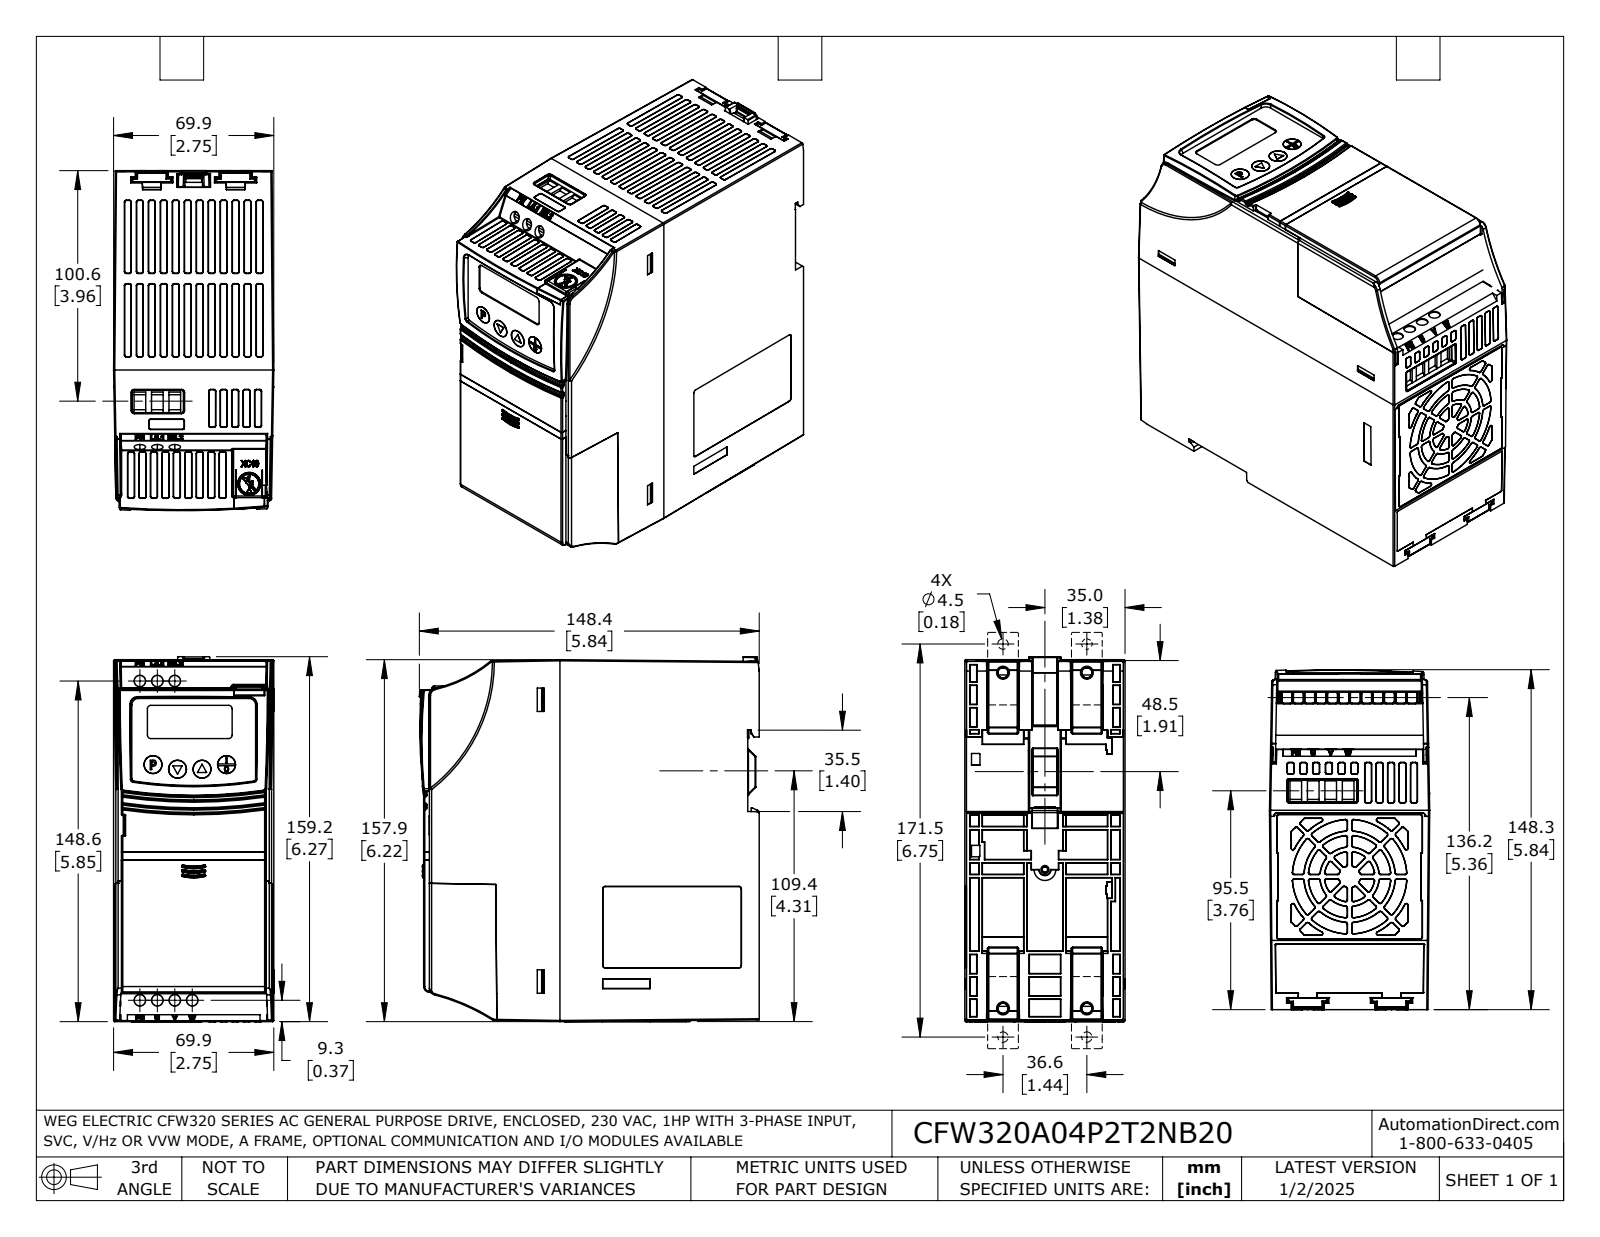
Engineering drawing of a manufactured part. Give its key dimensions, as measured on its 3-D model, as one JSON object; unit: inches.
{"part_name": "CFW320A04P2T2NB20", "step_written_by": "SolidWorks 2021 (AUTOMOTIVE_DESIGN)", "units": "inches", "bodies": {"solids": 6, "faces": 3715, "planar": 1587, "cylindrical": 853, "other": 1275}, "overall_size": [6.269, 5.841, 2.754], "volume_in3": 15.24, "surface_area_in2": 309, "round_holes": [[0.197, 3]], "partial_cylinders_radius": [[0.012, 327], [0.02, 150], [0.039, 13], [0.03, 5], [0.118, 3], [0.01, 2], [0.098, 1], [0.126, 1]], "face_to_face_distances": [0.07, 0.055, 0.019, 0.05, 6, 5.33, 5.275, 5.571, 5.516, 0.241], "hole_center_spacings": [0.3, 0.6]}
